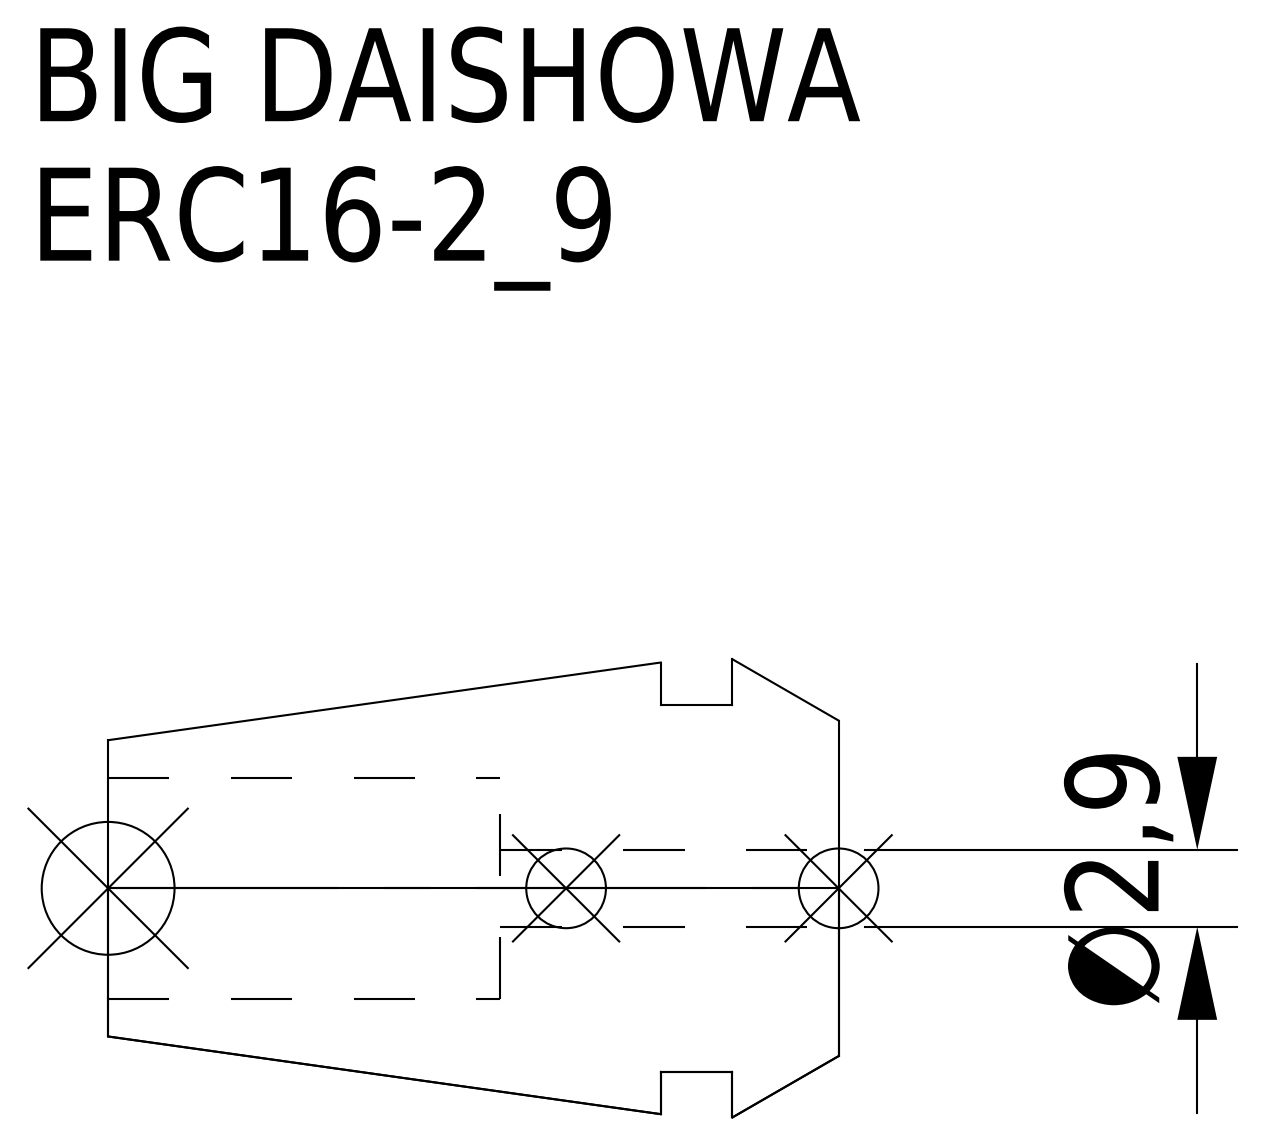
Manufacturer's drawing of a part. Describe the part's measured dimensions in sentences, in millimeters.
The part is named "ERC16-2_9". Its 3-D file was written by "CREO PARAMETRIC BY PTC INC, 2016380 (AUTOMOTIVE_DESIGN)". It is 1 solid with 15 faces: 5 planar, 6 cylindrical and 4 other. Overall it measures 27.5 by 17.25 by 17.25 millimeters. Its volume is 3 512 cubic millimeters and its surface area 2 135 square millimeters. Round holes: 1 of diameter 2.9, 1 of diameter 8.3. Round bosses or shafts: 1 of diameter 13.8. The main face-to-face distances are 4, 6.7, 2.7, 12.73, 8.73, 6.03, 27.5, 23.5, 20.8, 14.77.
